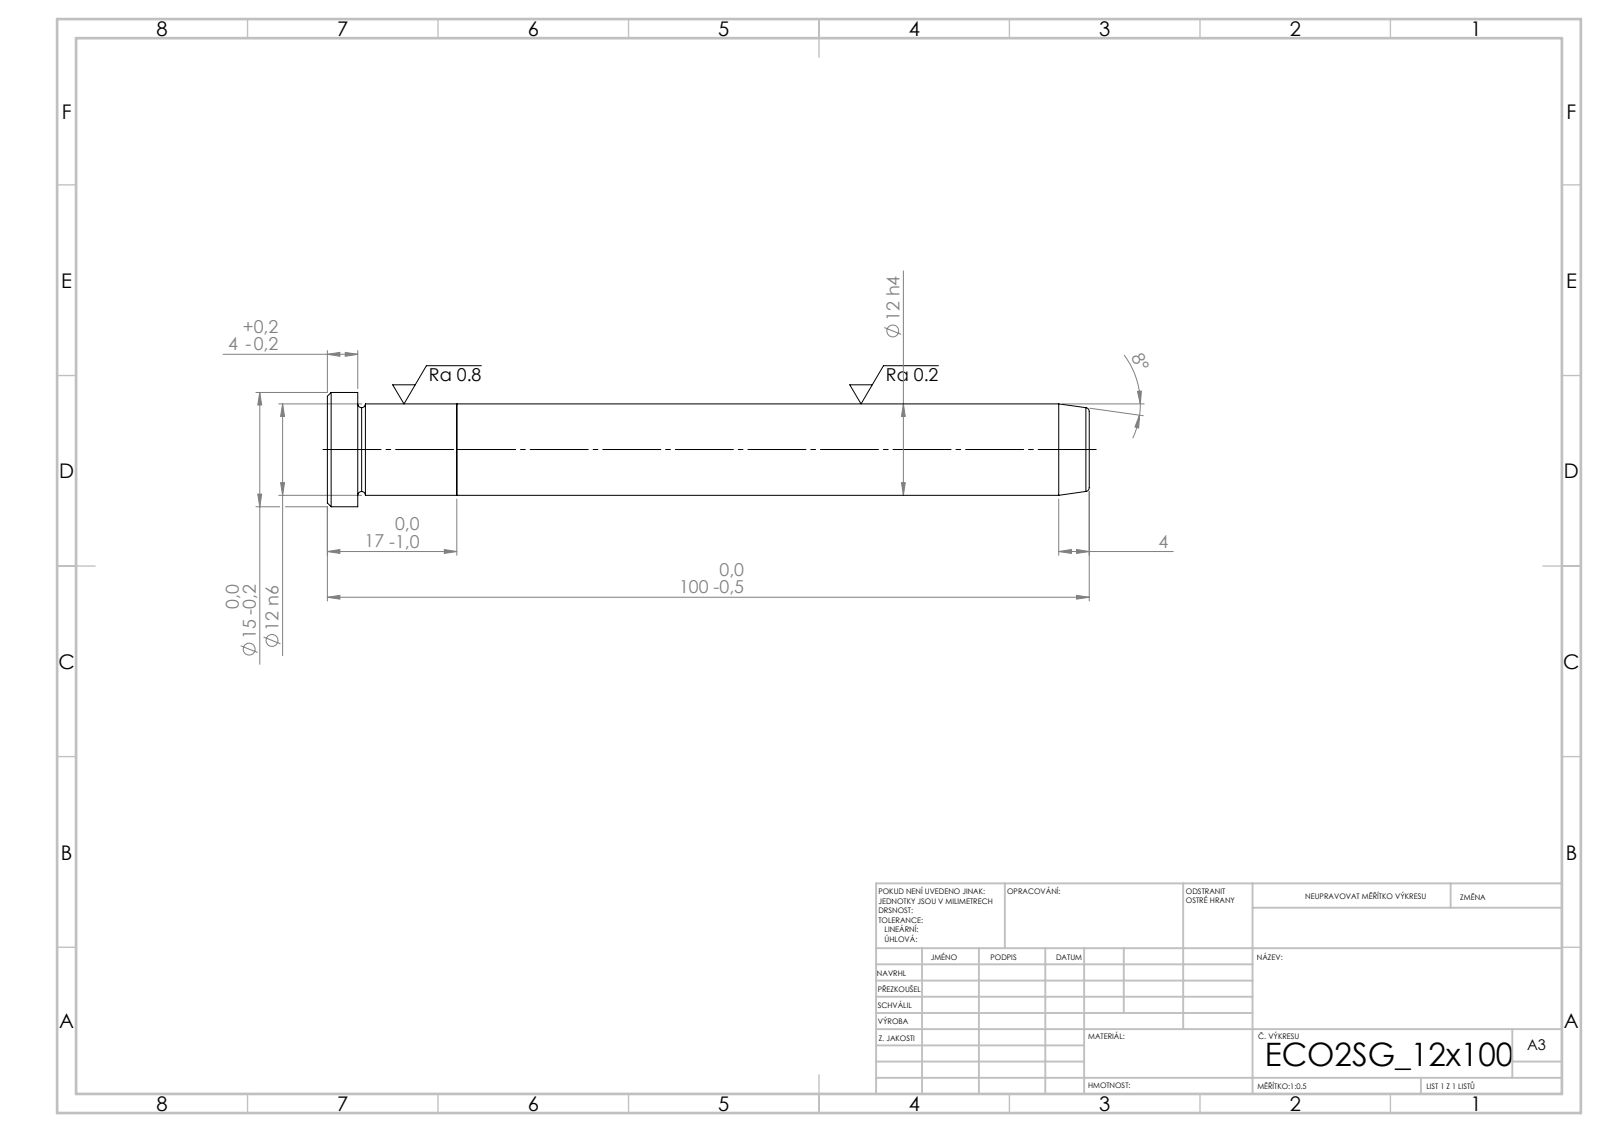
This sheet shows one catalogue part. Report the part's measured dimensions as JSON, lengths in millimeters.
{"step_written_by": "SolidWorks 2019 (CONFIG_CONTROL_DESIGN)", "units": "millimeters", "bodies": {"solids": 2, "faces": 21, "planar": 5, "cylindrical": 6, "other": 10}, "overall_size": [100, 15, 15], "volume_mm3": 11502, "surface_area_mm2": 4360, "round_bosses_or_shafts": [[15, 1], [12, 1]], "face_to_face_distances": [17, 83, 100, 96, 13, 4]}
